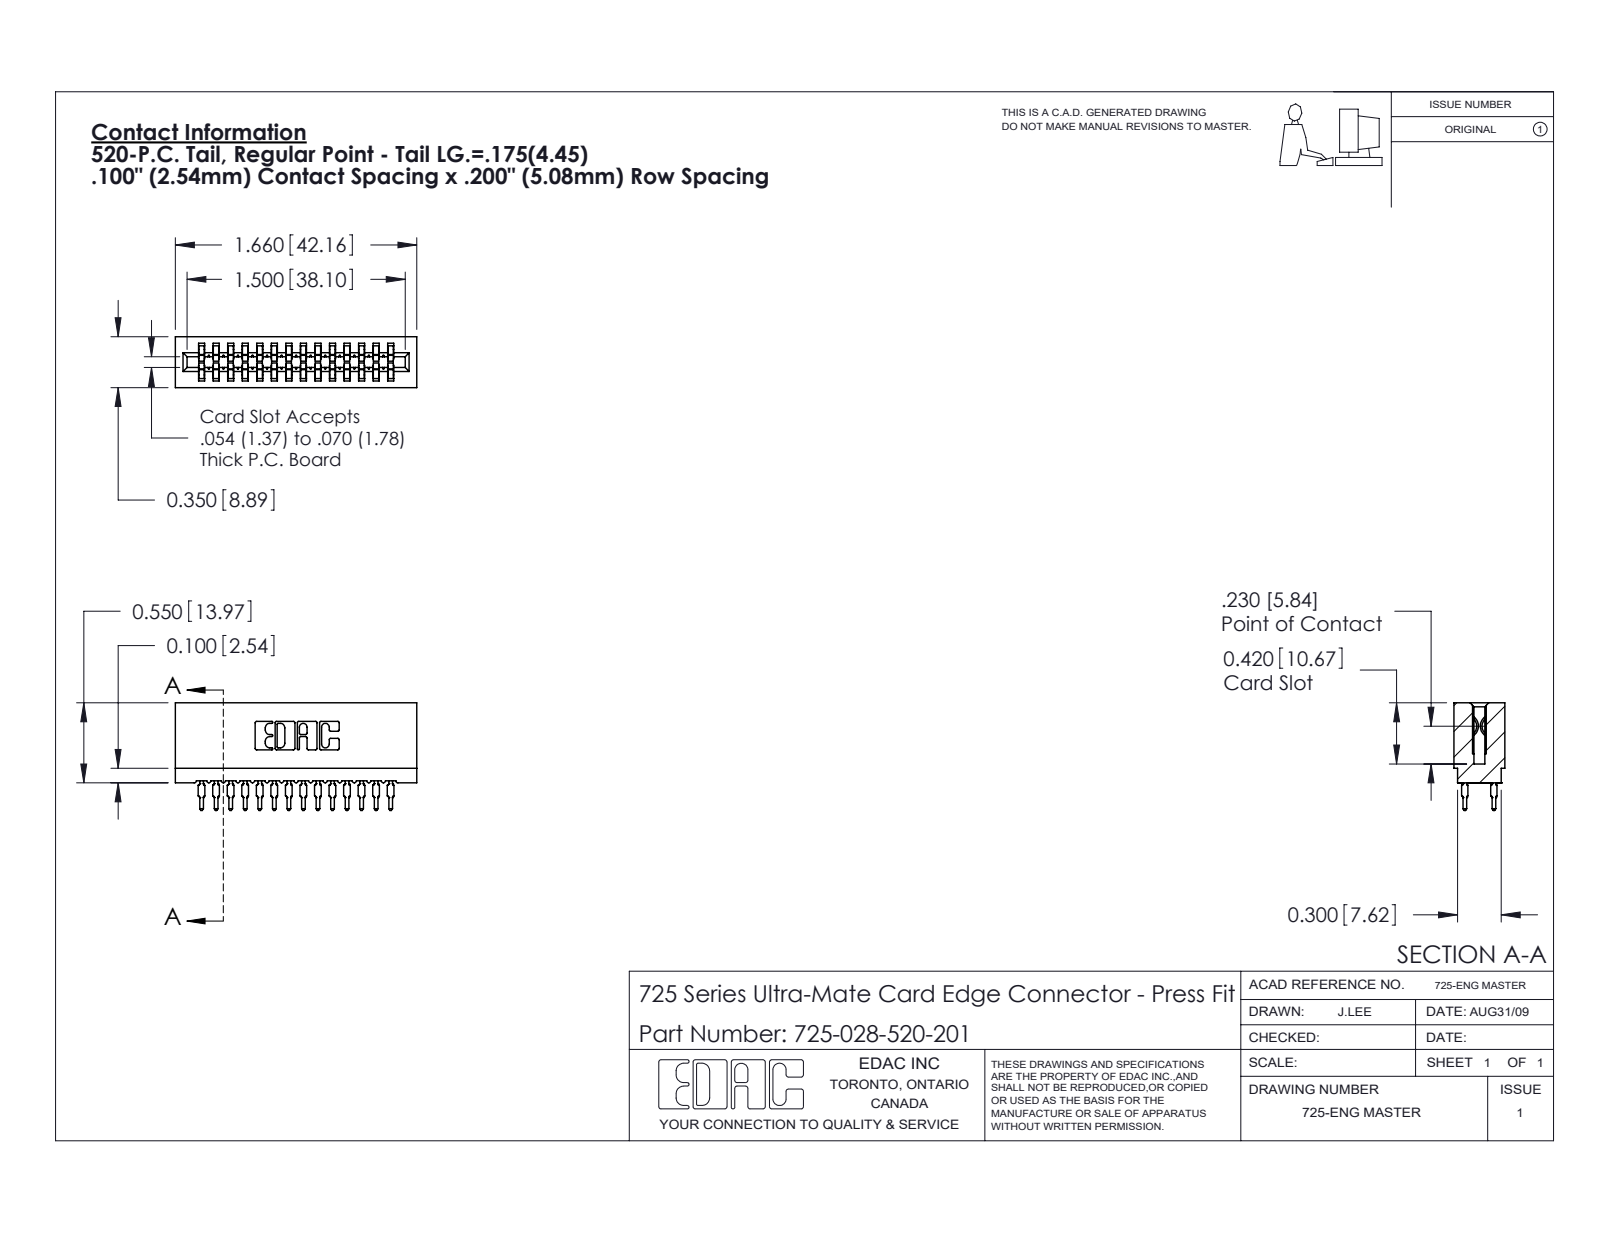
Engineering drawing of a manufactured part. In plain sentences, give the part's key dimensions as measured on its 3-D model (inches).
The part is named "745-292-001_520; 725-028-520-201; 725 Part_Insulator Option - 01". Its 3-D file was written by "SolidWorks 2020 (CONFIG_CONTROL_DESIGN)". It is 29 solids with 2601 faces: 1343 planar, 530 cylindrical and 728 other. Overall it measures 1.66 by 0.741 by 0.35 inches. Its volume is 0.211 cubic inches and its surface area 10.22 square inches. Partial cylindrical surfaces (rounded edges, fillets, slot ends): 56 of radius 0.021, 28 of radius 0.015, 22 of radius 0.01, 8 of radius 0.005, 8 of radius 0.011, 6 of radius 0.007, 6 of radius 0.031, 3 of radius 0.026. The main face-to-face distances are 0.1, 0.2, 0.6, 0.3, 0.4, 0.5, 0.7, 0.35, 0.212, 0.138.
